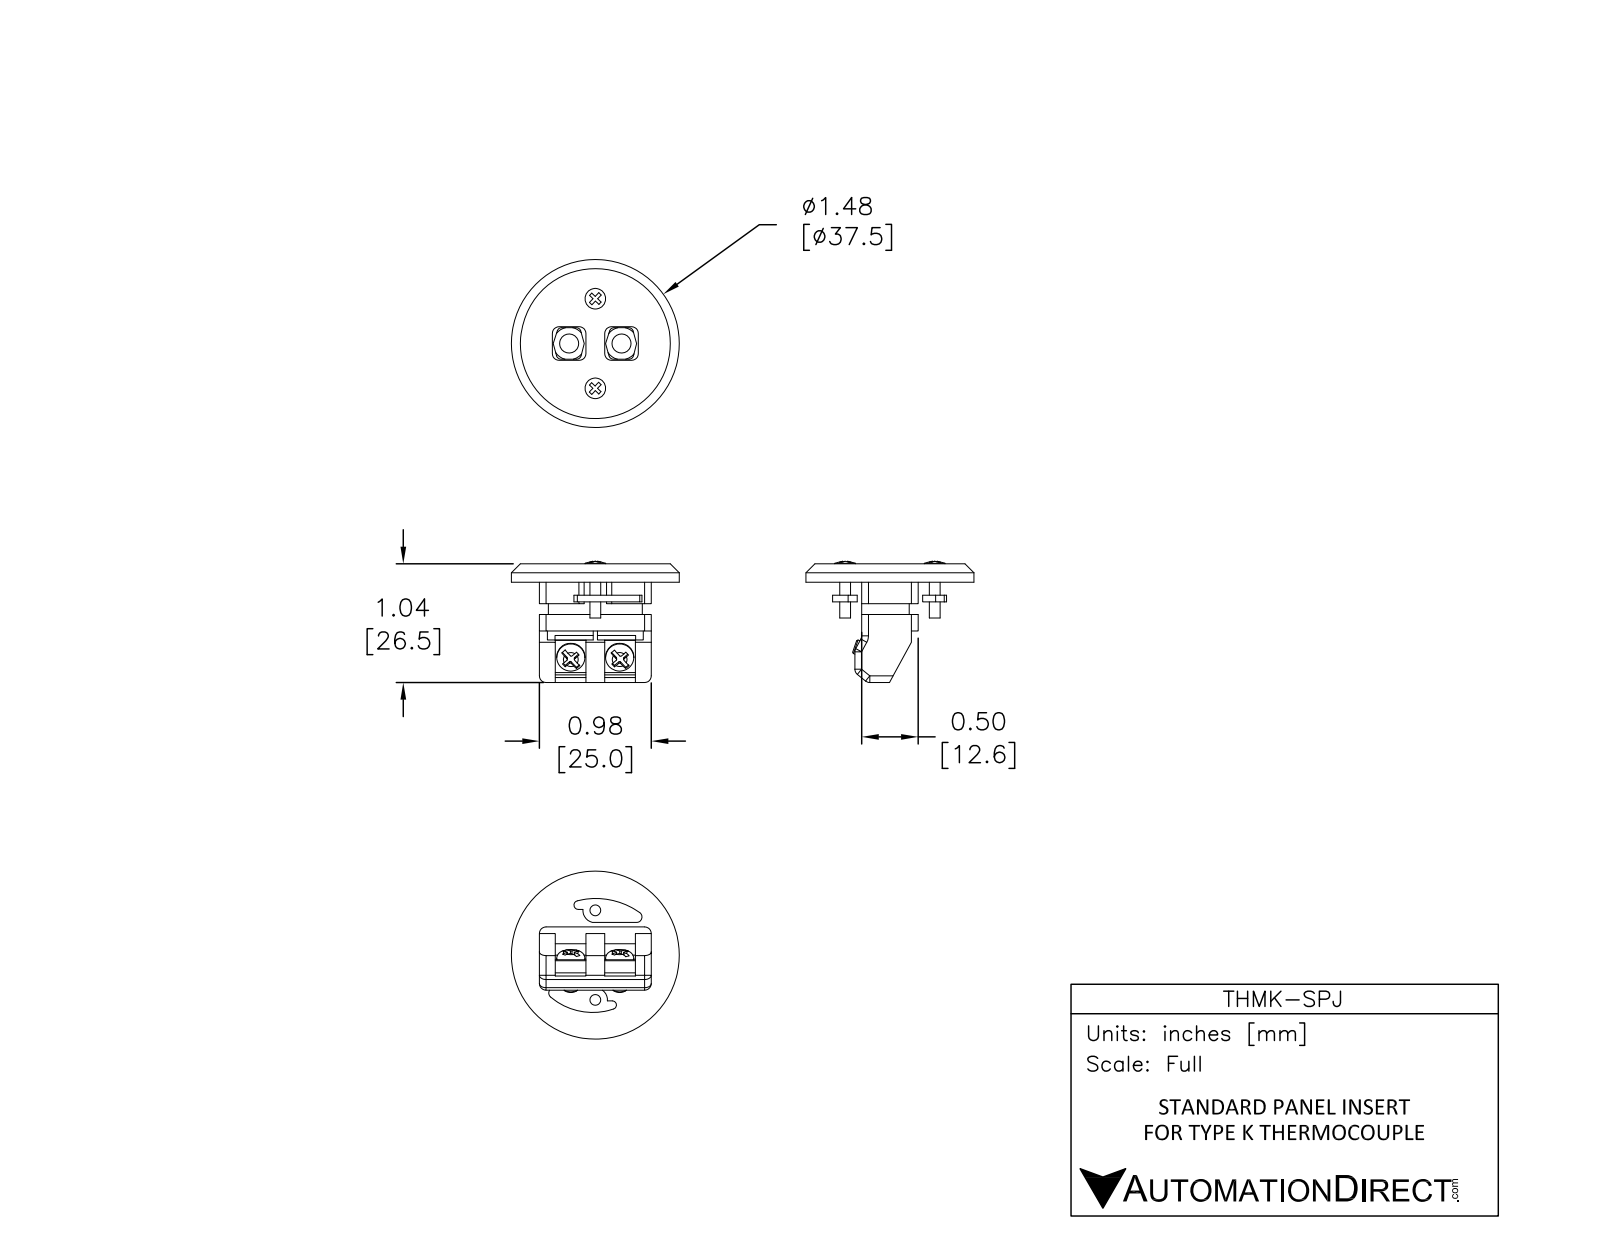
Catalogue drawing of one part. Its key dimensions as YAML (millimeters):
part_name: "THMK-SPJ"
step_written_by: "SolidWorks 2017 (AUTOMOTIVE_DESIGN)"
units: millimeters
bodies: {solids: 1, faces: 310, planar: 201, cylindrical: 85, other: 24}
overall_size: [37.5, 37.5, 27.06]
volume: 9567
surface_area: 5667
round_holes:
  - {diameter: 4.25, count: 2}
round_bosses_or_shafts:
  - {diameter: 6.3, count: 2}
  - {diameter: 4.6, count: 2}
  - {diameter: 3.2, count: 2}
  - {diameter: 2.4, count: 2}
  - {diameter: 37.5, count: 1}
partial_cylinders:
  - {radius: 1.5, count: 24}
  - {radius: 0.25, count: 8}
  - {radius: 1, count: 8}
  - {radius: 0.92, count: 1}
  - {radius: 0.98, count: 1}
  - {radius: 1.16, count: 1}
  - {radius: 1.22, count: 1}
  - {radius: 2.7, count: 1}
face_to_face_distances: [4.1, 2, 12.6, 25, 1.5, 7, 10.9, 15, 8.5, 1]
hole_center_spacings: [11.7]
